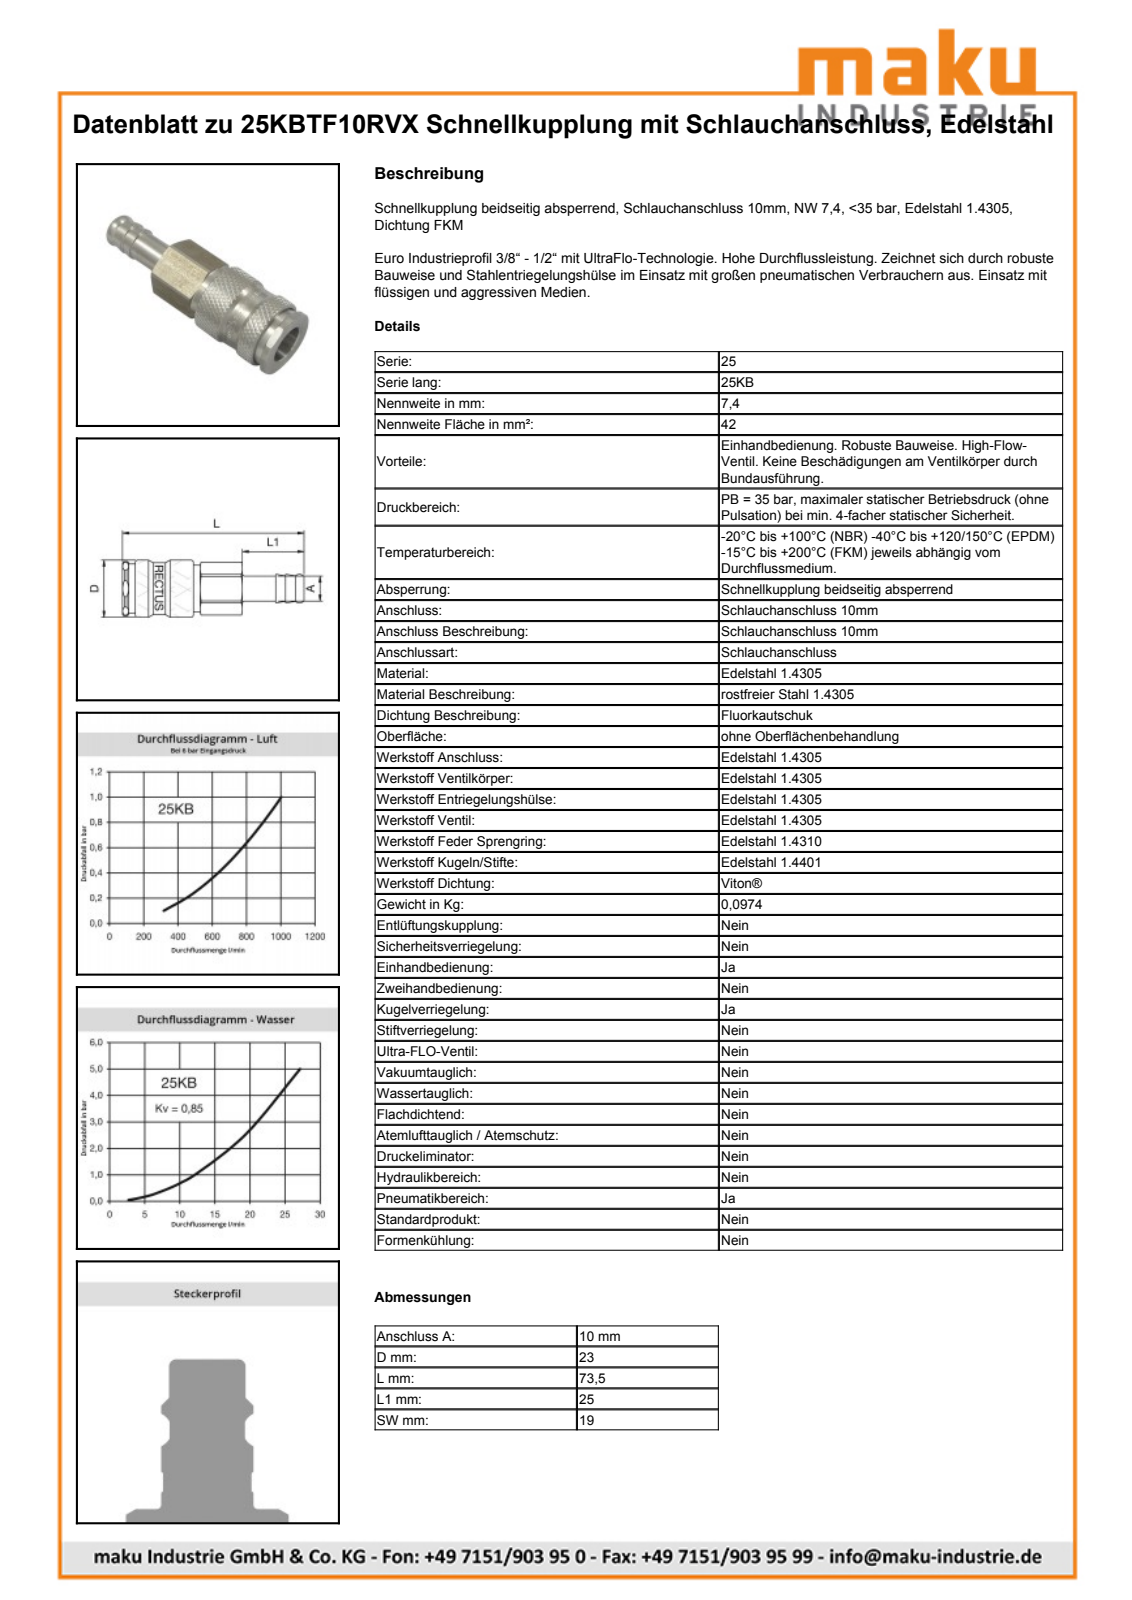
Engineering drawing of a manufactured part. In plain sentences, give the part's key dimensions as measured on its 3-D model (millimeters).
The part is named "D113255". Its 3-D file was written by "Autodesk Inventor 2013 (AUTOMOTIVE_DESIGN)". It is 2 solids with 608 faces: 240 planar, 82 cylindrical and 286 other. Overall it measures 73.5 by 23.15 by 23.15 millimeters. Its volume is 18 008 cubic millimeters and its surface area 8 547 square millimeters. Round holes: 1 of diameter 15.1, 1 of diameter 16, 1 of diameter 17.25, 1 of diameter 19.35, 1 of diameter 20.05. Round bosses or shafts: 1 of diameter 23.15, 1 of diameter 22, 1 of diameter 21, 1 of diameter 20, 1 of diameter 18.95, 1 of diameter 15.3, 1 of diameter 15, 1 of diameter 14.47. Partial cylindrical surfaces (rounded edges, fillets, slot ends): 1 of radius 10.4, 1 of radius 10.7. The main face-to-face distances are 19, 48.5, 24.5, 24, 73.5, 49, 25, 5.25, 19.25, 28.75.
